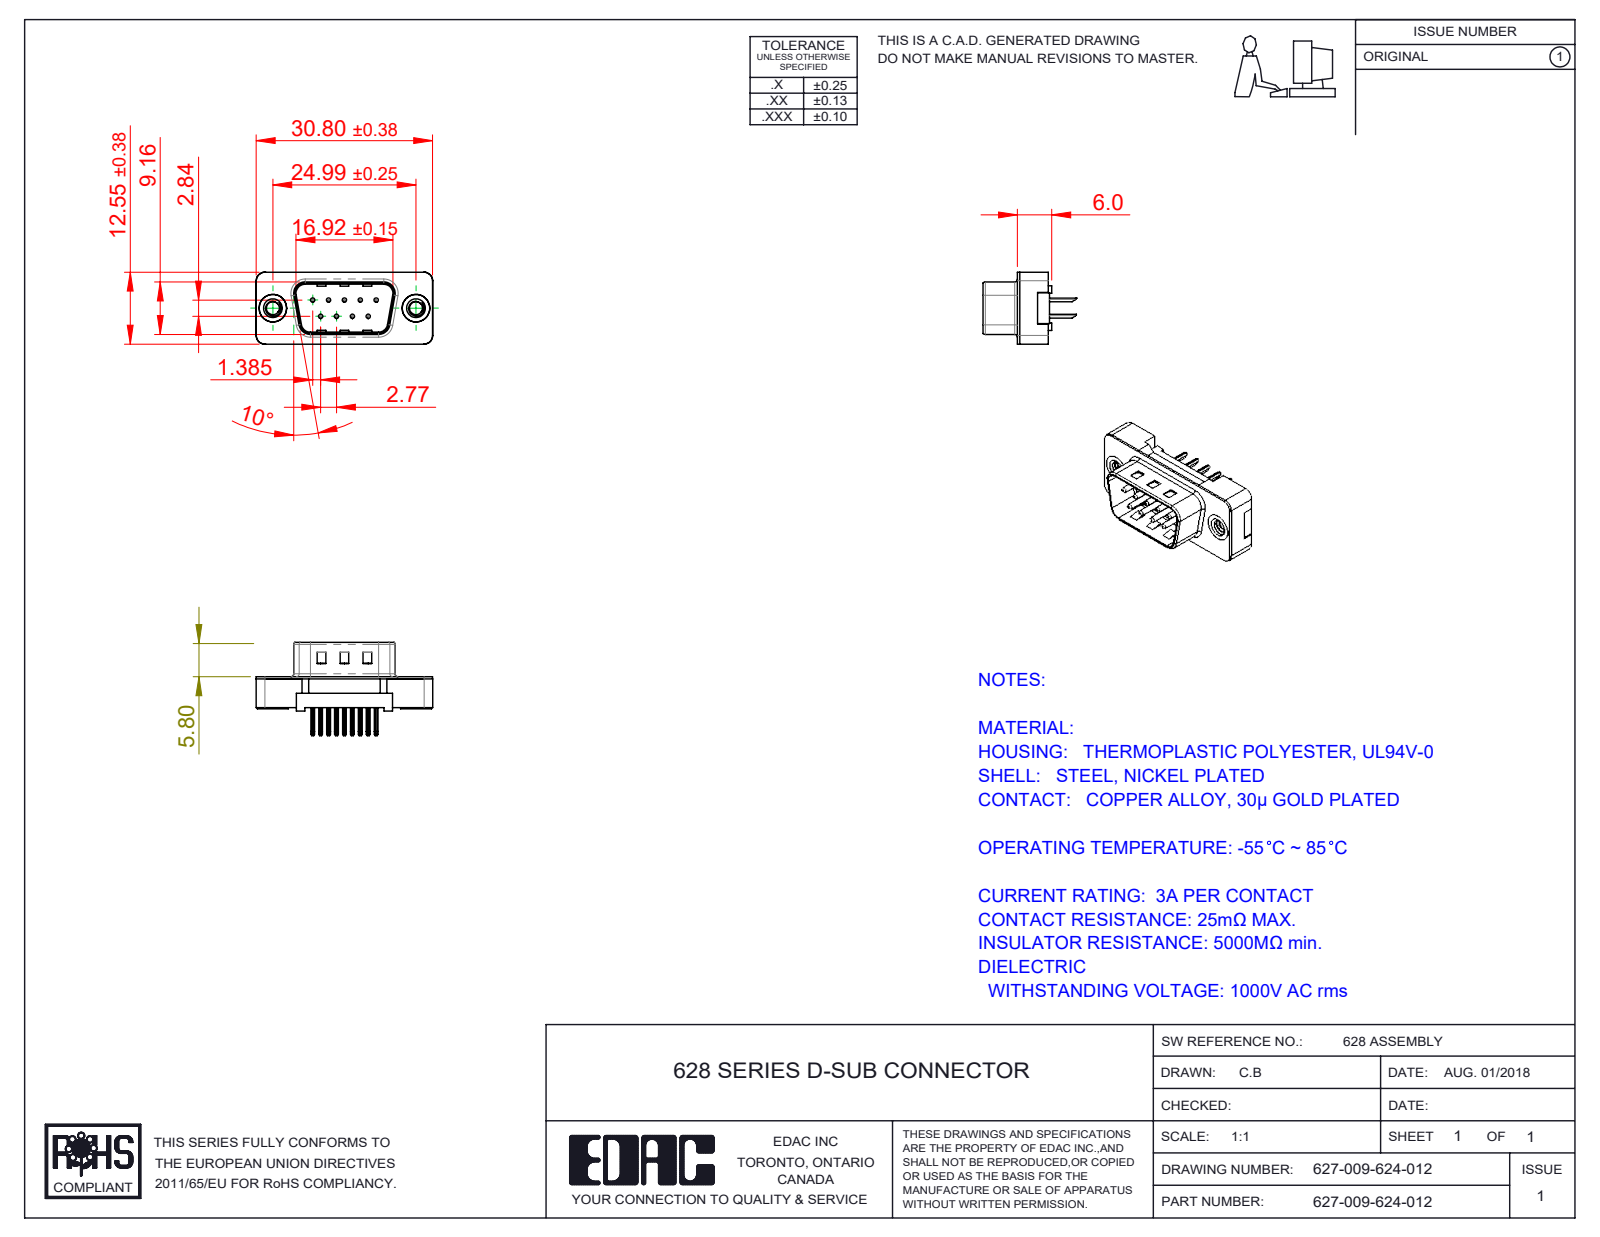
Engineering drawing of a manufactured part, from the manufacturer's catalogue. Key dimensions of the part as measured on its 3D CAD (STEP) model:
Part name (STEP PRODUCT): 627 PB Contact Row 2_24; 627-009-624-012; 627 Plastic Body Housing_09 Contacts; 627 PB Shell_09 Contacts (+2 more)
STEP written by: SolidWorks 2020 (CONFIG_CONTROL_DESIGN)
Units: millimetres
Bodies: 13 solids, 783 faces (481 planar, 240 cylindrical, 62 other)
Overall size (bounding box): 30.81 × 16.3 × 12.55
Volume: 1 651 mm³ · Surface area: 3 404 mm²
Round holes (diameter × count): ⌀0.35 ×9, ⌀0.85 ×9, ⌀2.26 ×2, ⌀4 ×2, ⌀4.8 ×2, ⌀5 ×2
Round bosses / shafts (diameter × count): ⌀0.75 ×9, ⌀4.9 ×2
Partial cylindrical surfaces — rounded edges, fillets, slot ends (radius × count): R0.25 ×18, R0.12 ×9, R0.5 ×8, R1.5 ×7, R0.9 ×4, R1.6 ×4, R2 ×4, R0.4 ×2
Main face-to-face distances: 0.4, 2.5, 5.4, 5, 2.9, 8.76, 2.1, 8.08, 0.68, 8.48
Hole centre spacings: 3.16, 2.77, 5.04, 5.54, 7.49, 5.03, 7.09, 8.31
